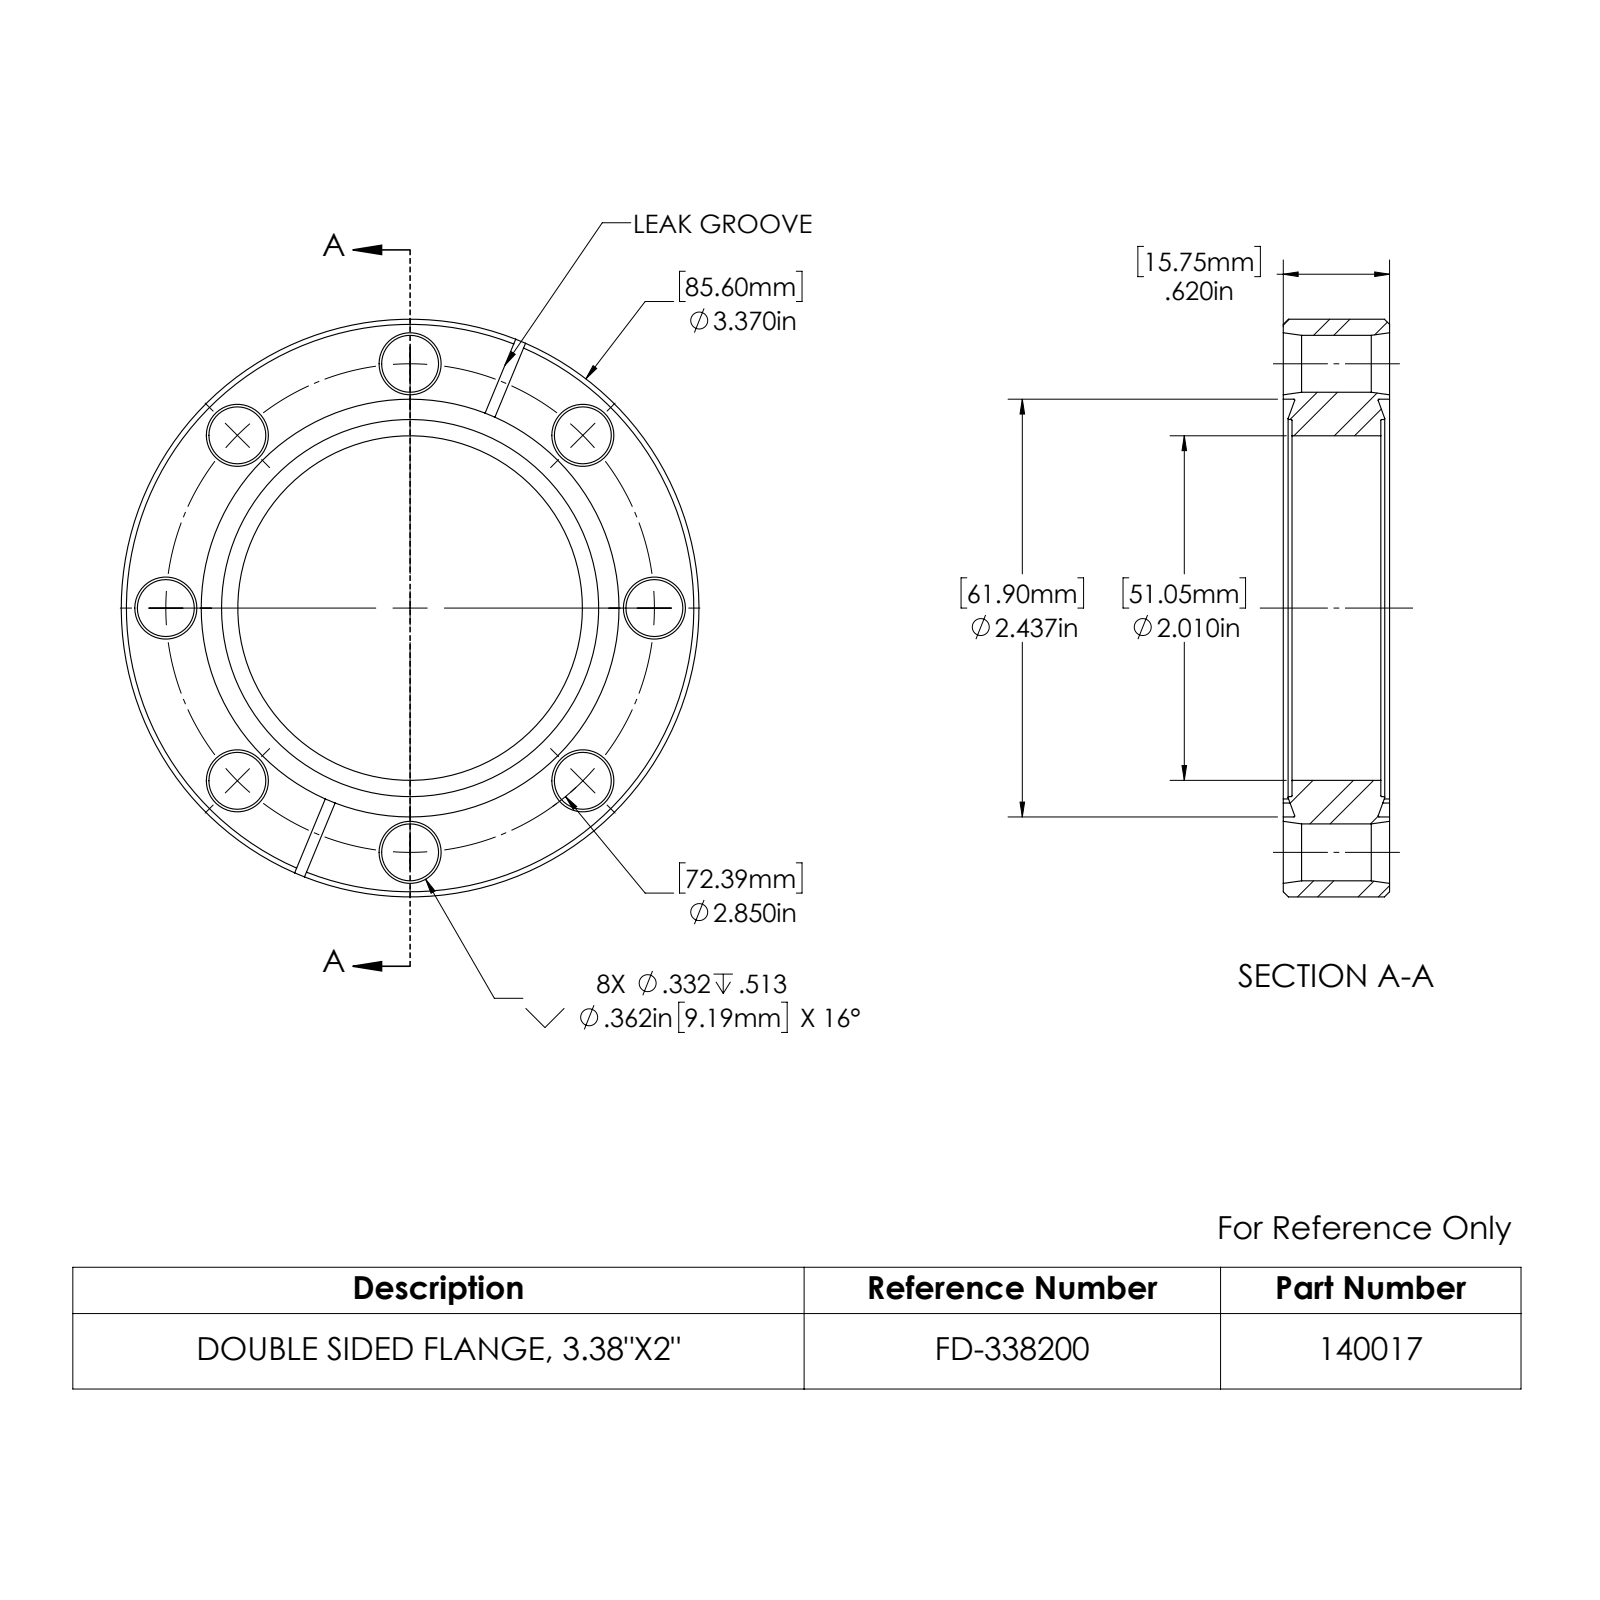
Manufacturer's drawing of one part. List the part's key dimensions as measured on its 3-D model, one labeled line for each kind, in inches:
Part name (STEP PRODUCT): 140017
STEP written by: SolidWorks 2022 (AUTOMOTIVE_DESIGN)
Units: inches
Bodies: 1 solid, 100 faces (14 planar, 32 cylindrical, 54 other)
Overall size (bounding box): 3.37 × 3.37 × 0.62
Volume: 2.951 in³ · Surface area: 26.3 in²
Round holes (diameter × count): ⌀0.332 ×8, ⌀2.01 ×1, ⌀2.2 ×1, ⌀2.437 ×1
Round bosses / shafts (diameter × count): ⌀3.37 ×1
Partial cylindrical surfaces — rounded edges, fillets, slot ends (radius × count): R1.25 ×4
Main face-to-face distances: 0.62, 0.051, 0.569, 0.518, 0.062, 0.061, 0.063
Hole centre spacings: 1.091, 2.633, 1.425, 1.425, 2.015, 2.015, 2.85, 2.85
